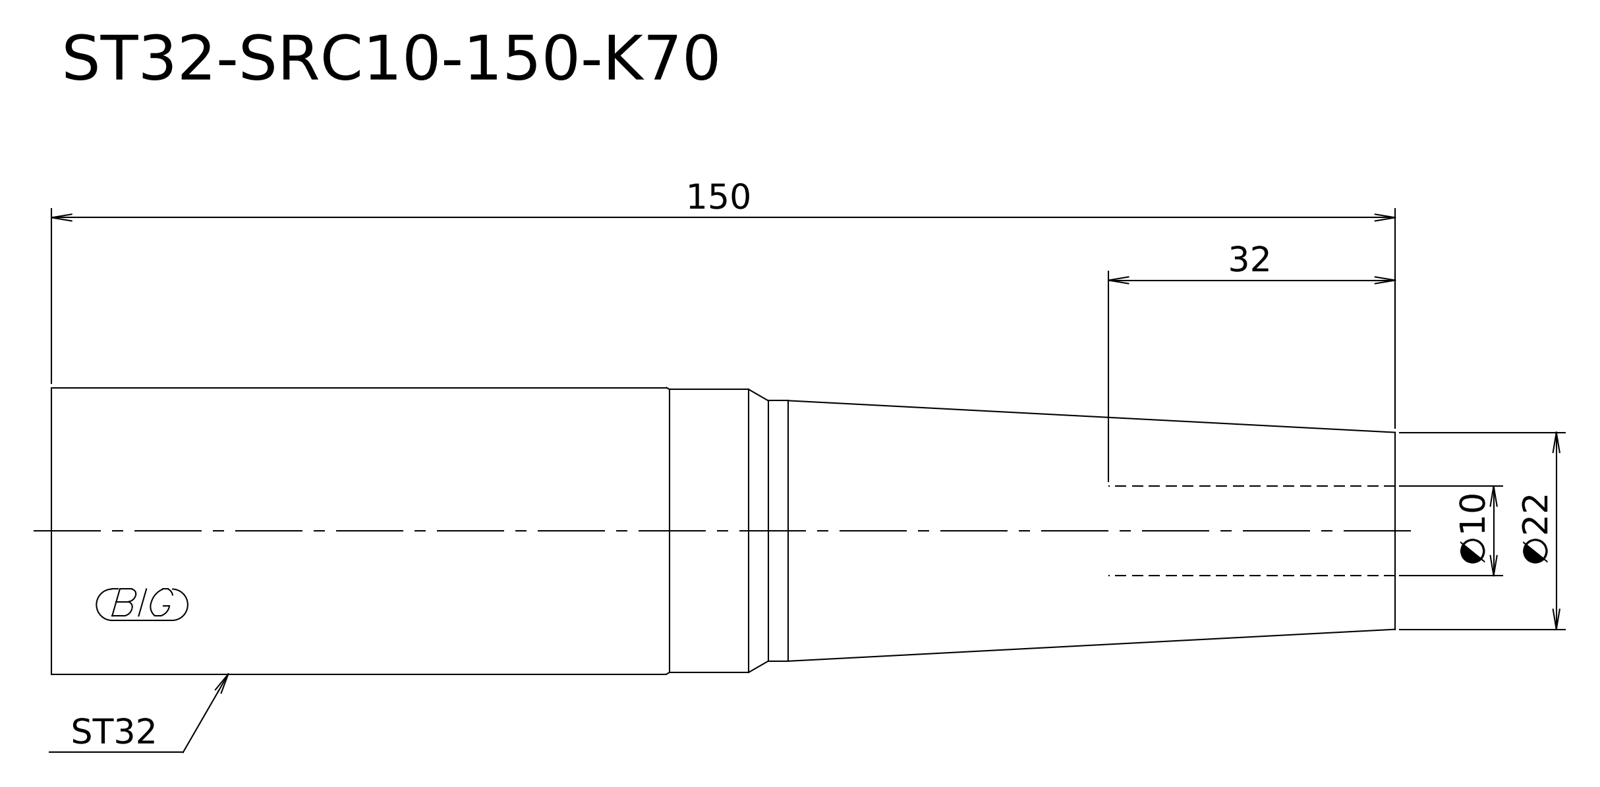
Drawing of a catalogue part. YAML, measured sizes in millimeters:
step_written_by: "Kubotek KeyCreator V8.5.1 (14335) (CONFIG_CONTROL_DESIGN)"
units: millimeters
bodies: {solids: 1, faces: 8, planar: 2, cylindrical: 3, other: 3}
overall_size: [150, 32, 32]
volume: 100444
surface_area: 14893
round_bosses_or_shafts:
  - {diameter: 32, count: 1}
  - {diameter: 31.6, count: 1}
  - {diameter: 29.1, count: 1}
face_to_face_distances: [150]
